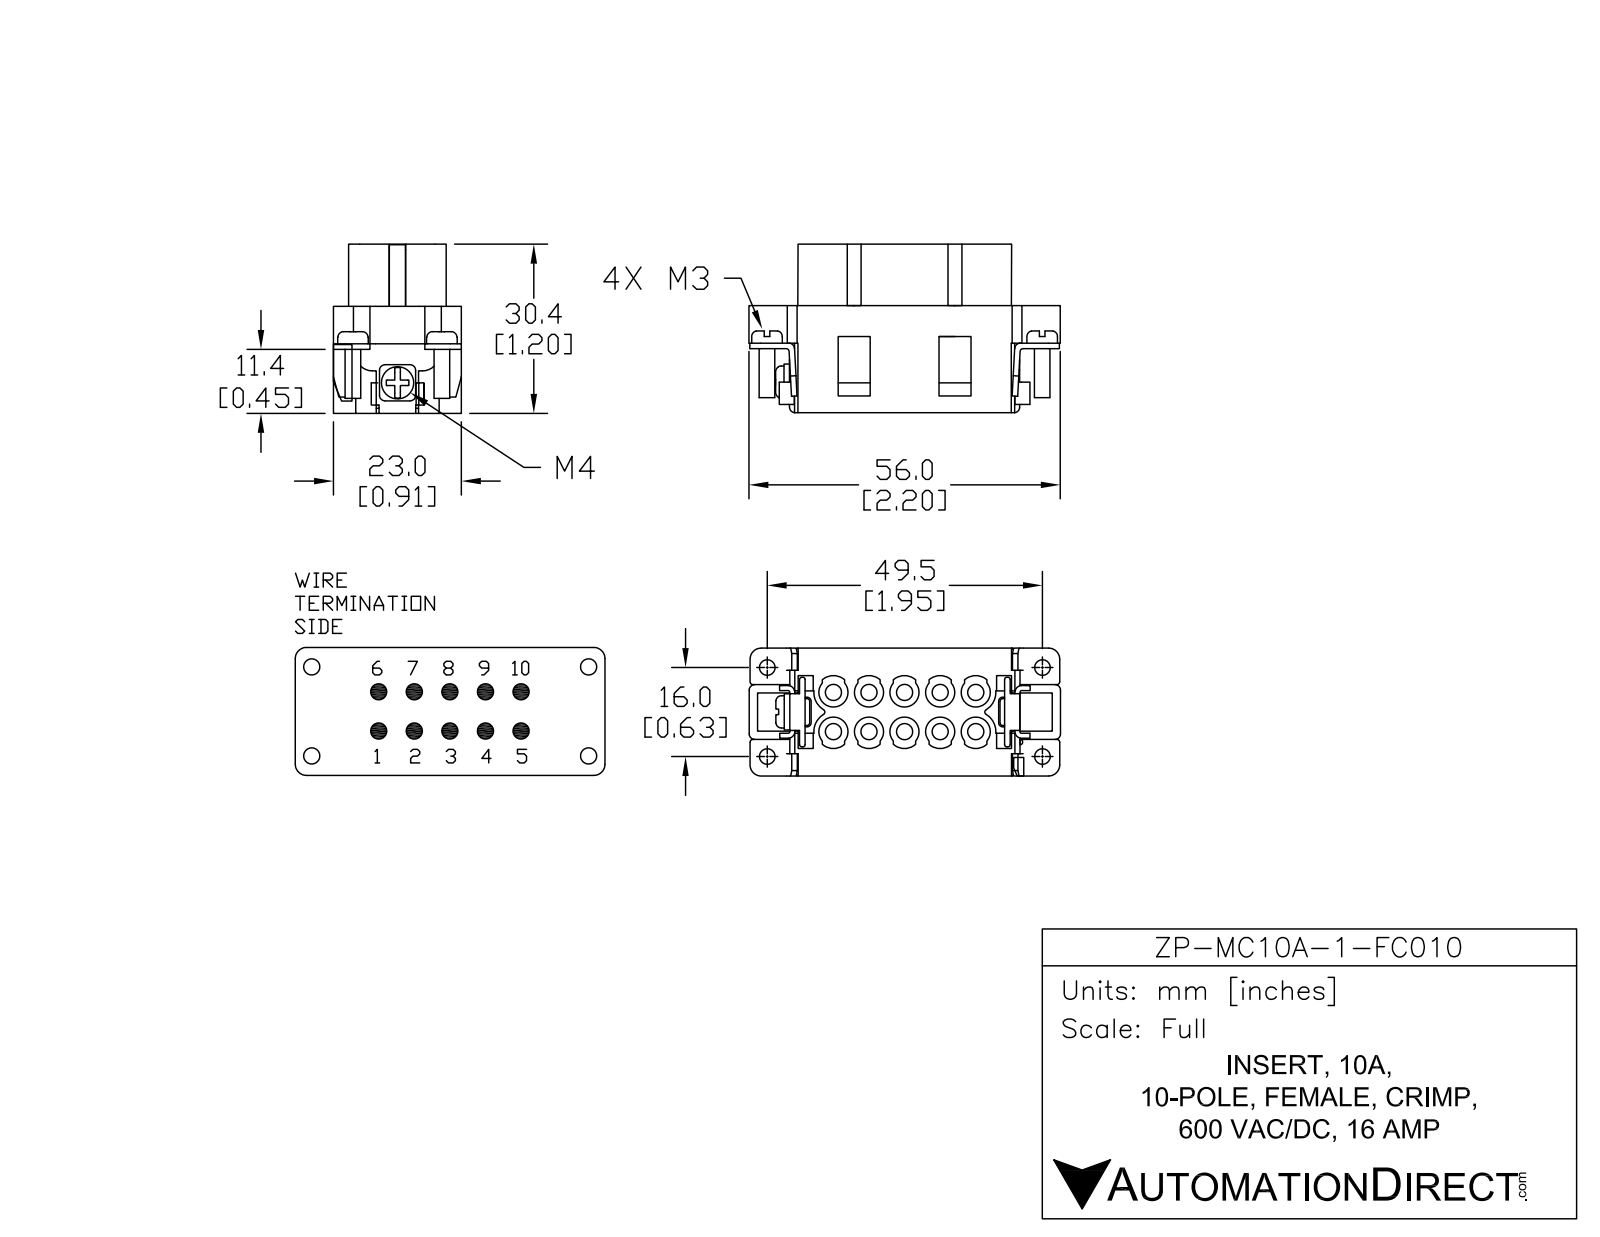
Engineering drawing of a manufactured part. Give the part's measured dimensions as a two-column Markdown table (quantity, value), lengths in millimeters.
| quantity | value |
| --- | --- |
| part name | ZP-MC10A-1-FC010 |
| STEP written by | SolidWorks 2014 (AUTOMOTIVE_DESIGN) |
| units | millimeters |
| bodies | 7 solids, 627 faces (409 planar, 208 cylindrical, 10 other) |
| overall size | 56 × 30.5 × 23 |
| volume | 19 287 mm³ |
| surface area | 14 674 mm² |
| round holes (diameter × count) | 2.9 × 10, 2.15 × 4, 2.85 × 1 |
| round bosses / shafts (diameter × count) | 4.9 × 6, 5.5 × 4, 2.8 × 4, 5.8 × 1 |
| partial cylindrical surfaces (radius × count) | 0.25 × 20, 0.5 × 19, 1 × 12, 2.62 × 10, 3.03 × 10, 0.4 × 8, 0.75 × 8, 1.4 × 8 |
| main face-to-face distances | 2.72, 20.28, 23, 19.25, 1, 3.5, 1.5, 11.25, 30.5, 17.56 |
| hole center spacings | 4.76, 10.23, 6.4, 9.53, 12.8, 16.38, 14.62, 7.06 |
